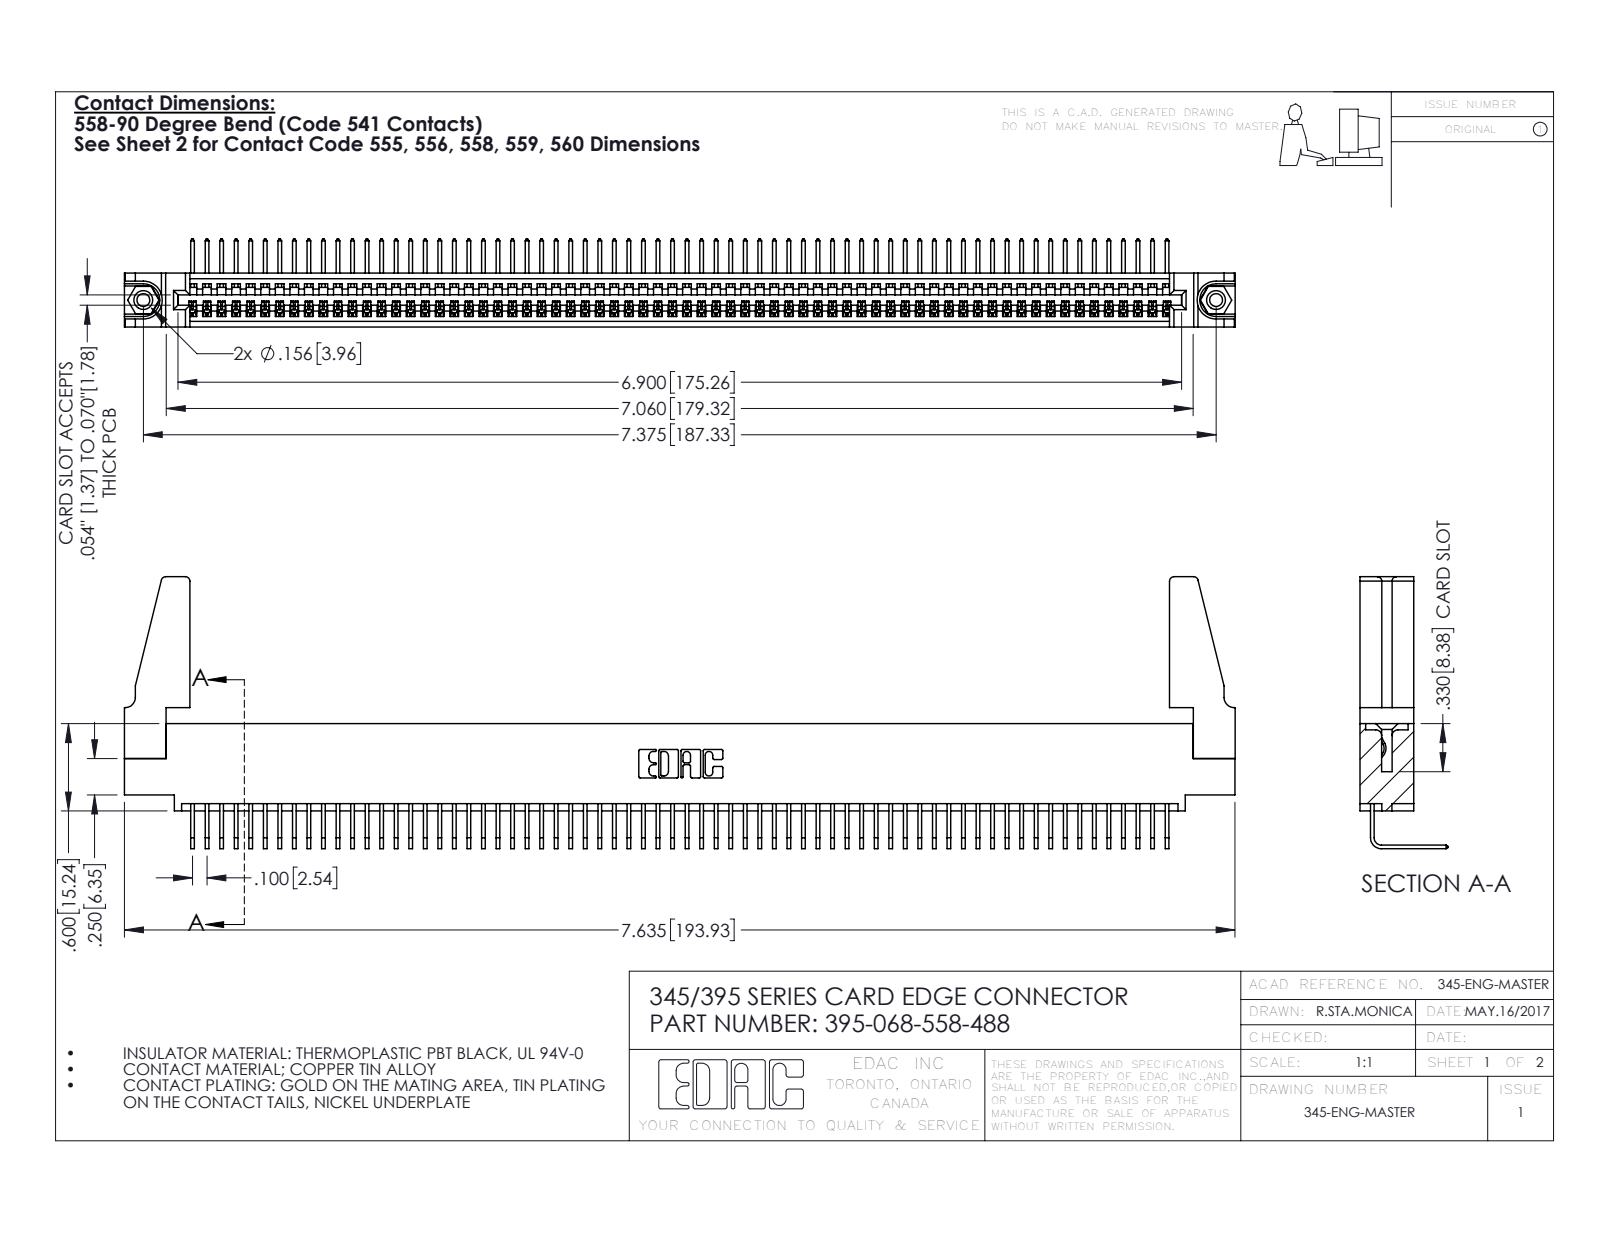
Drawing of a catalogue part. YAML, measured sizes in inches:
part_name: "345-292-001_558 Tail - 2; 345-220-078_345-220-088; 395-068-558-488; 345-250-001_345-250-001-102 (+1 more)"
step_written_by: "SolidWorks 2016 (CONFIG_CONTROL_DESIGN)"
units: inches
bodies: {solids: 73, faces: 4334, planar: 3012, cylindrical: 1306, other: 16}
overall_size: [7.636, 1.869, 0.605]
volume: 1.345
surface_area: 46.29
round_holes:
  - {diameter: 0.089, count: 2}
  - {diameter: 0.125, count: 2}
  - {diameter: 0.156, count: 2}
  - {diameter: 0.064, count: 1}
round_bosses_or_shafts:
  - {diameter: 0.155, count: 2}
partial_cylinders:
  - {radius: 0.006, count: 136}
  - {radius: 0.01, count: 22}
  - {radius: 0.03, count: 8}
  - {radius: 0.007, count: 6}
  - {radius: 0.031, count: 6}
  - {radius: 0.026, count: 3}
  - {radius: 0.031, count: 2}
  - {radius: 0.04, count: 2}
face_to_face_distances: [0.072, 0.298, 0.37, 0.098, 0.272, 0.025, 0.2, 0.225, 0.149, 0.072]
hole_center_spacings: [0.27, 7.139, 7.375]
